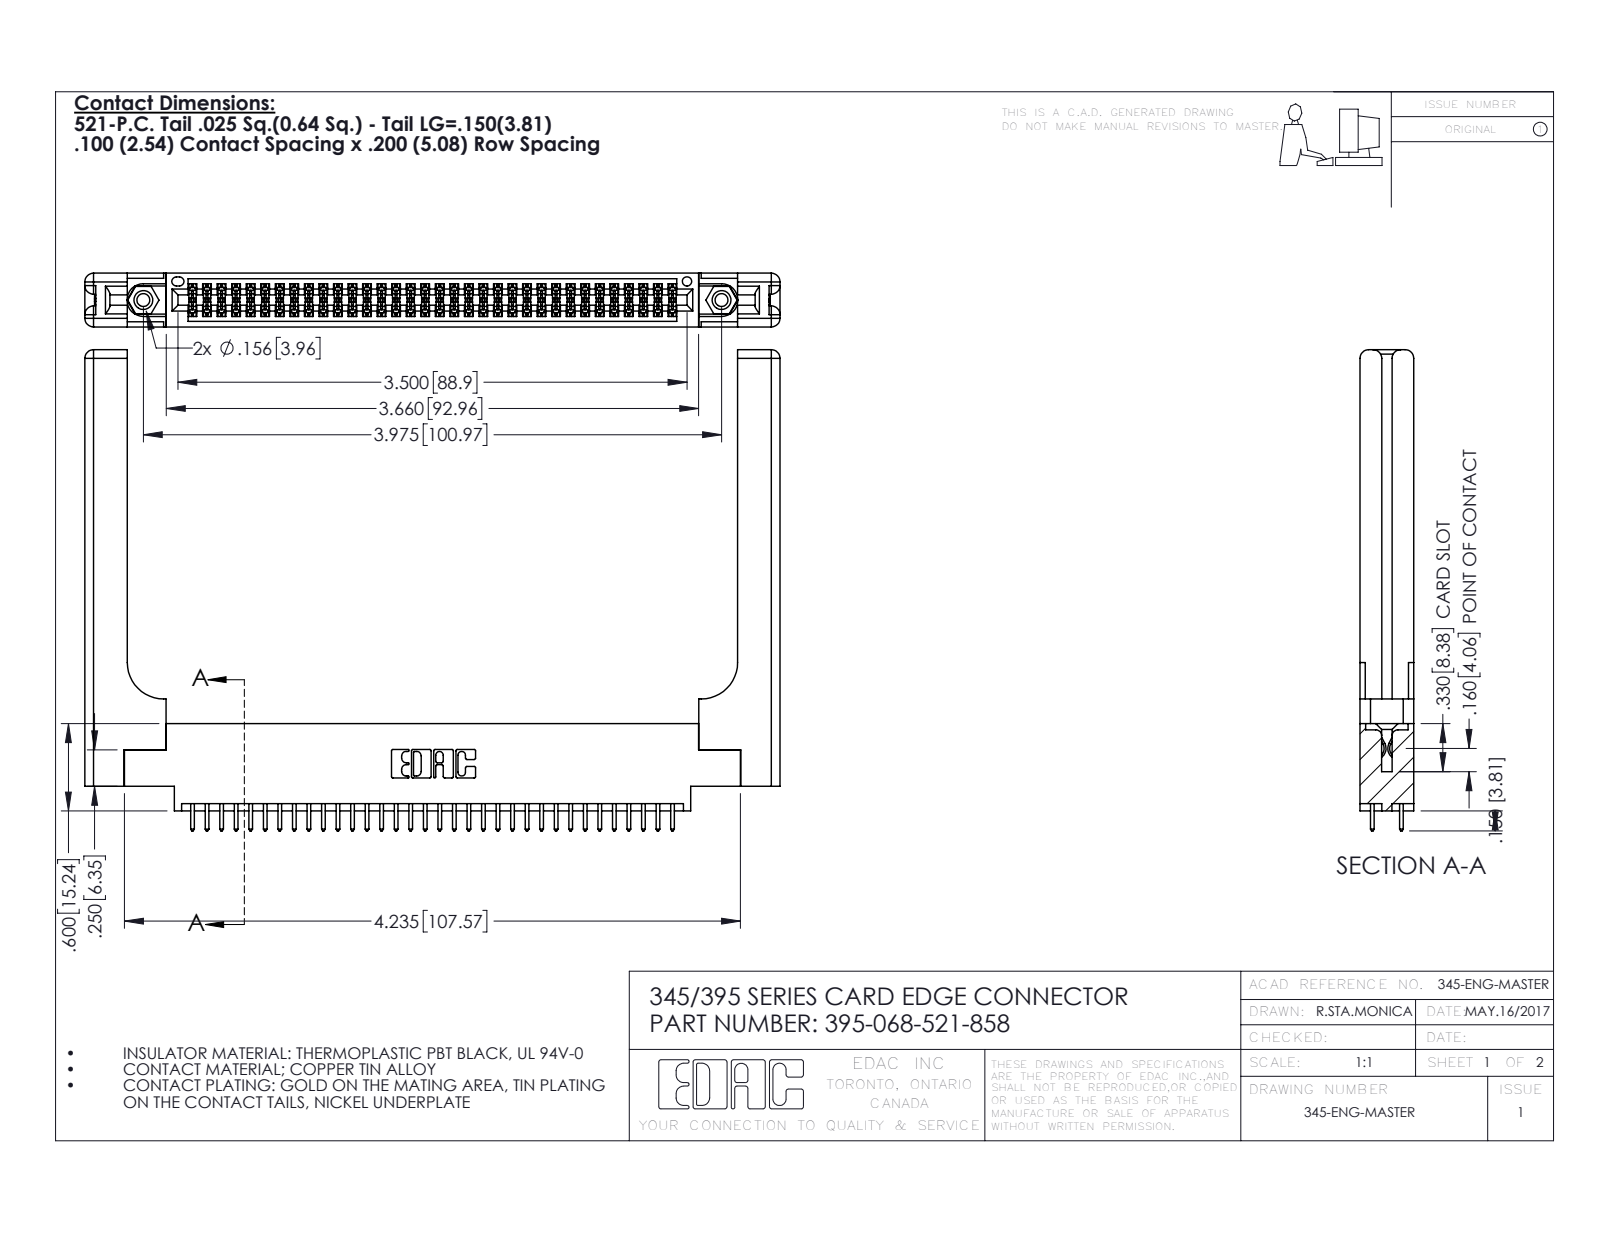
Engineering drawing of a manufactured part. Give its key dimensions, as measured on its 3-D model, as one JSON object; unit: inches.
{"part_name": "345-292-001_345-293-121; 395-068-521-858; 345-250-001_345-250-001-102; 345 Part_0.170 Offset - 0.156 Dia-TH (+1 more)", "step_written_by": "SolidWorks 2016 (CONFIG_CONTROL_DESIGN)", "units": "inches", "bodies": {"solids": 73, "faces": 3786, "planar": 2476, "cylindrical": 1250, "other": 60}, "overall_size": [4.779, 3.307, 0.37], "volume_in3": 1.224, "surface_area_in2": 34.07, "round_holes": [[0.089, 2], [0.125, 2], [0.156, 2], [0.064, 1]], "round_bosses_or_shafts": [[0.155, 2]], "partial_cylinders_radius": [[0.006, 102], [0.01, 68], [0.01, 22], [0.06, 16], [0.007, 6], [0.031, 6], [0.026, 3], [0.014, 2]], "face_to_face_distances": [0.37, 0.072, 0.298, 0.098, 0.272, 0.025, 0.2, 0.225, 0.148, 0.15], "hole_center_spacings": [0.27, 3.74, 3.975]}
